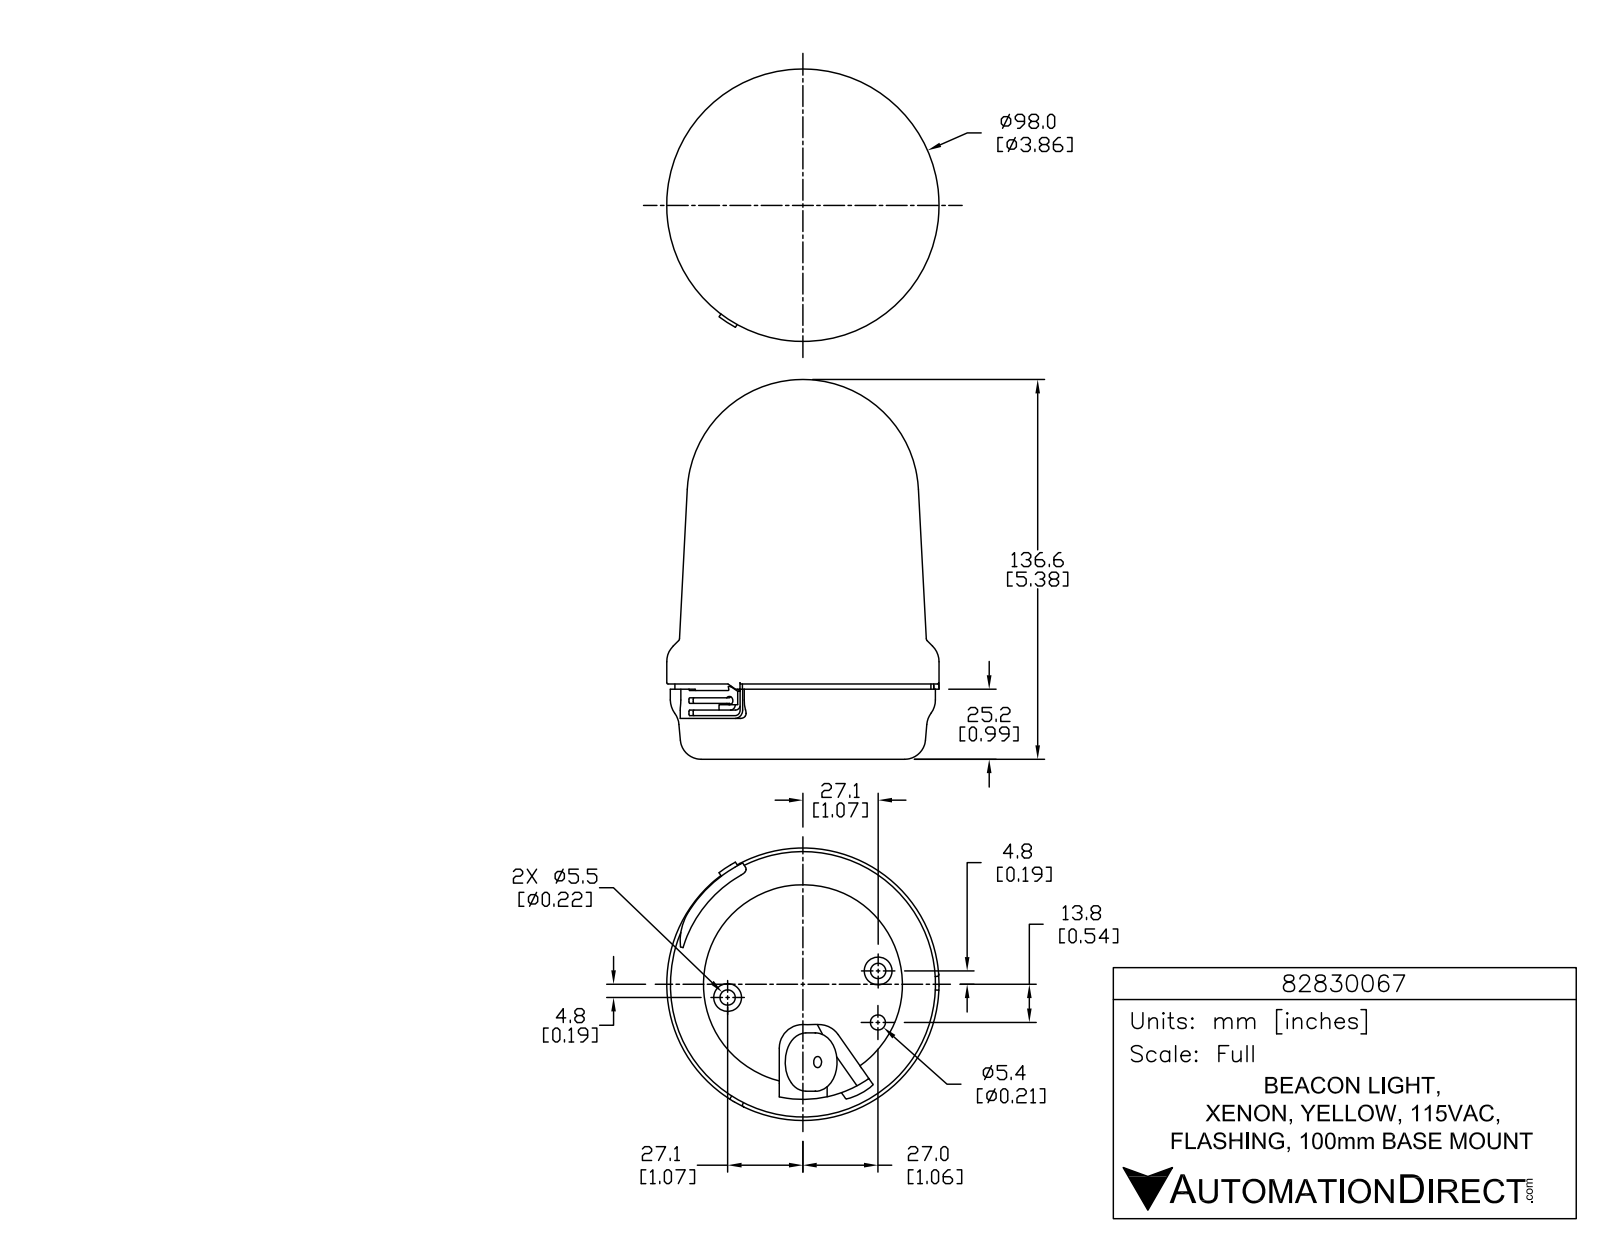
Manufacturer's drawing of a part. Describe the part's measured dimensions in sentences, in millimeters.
The part is named "82830067". Its 3-D file was written by "SolidWorks 2015 (AUTOMOTIVE_DESIGN)". It is 1 solid with 872 faces: 566 planar, 204 cylindrical and 102 other. Overall it measures 136.6 by 98 by 98 millimeters. Its volume is 732 300 cubic millimeters and its surface area 47 520 square millimeters. Round holes: 3 of diameter 1.5, 2 of diameter 5.5, 1 of diameter 4, 1 of diameter 5.4, 1 of diameter 71.6. Round bosses or shafts: 3 of diameter 8.6, 3 of diameter 2.1, 2 of diameter 10, 1 of diameter 98, 1 of diameter 95.4, 1 of diameter 92.1, 1 of diameter 21. Partial cylindrical surfaces (rounded edges, fillets, slot ends): 9 of radius 0.1, 6 of radius 0.1, 6 of radius 0.3, 6 of radius 0.3, 6 of radius 0.3, 6 of radius 5, 5 of radius 0.5, 4 of radius 1. The main face-to-face distances are 26.5, 24.7, 1.9, 0.5, 25.2, 27.1, 6, 14.7, 14.2, 10.5. The hole center spacings are 27.5, 18.5, 30.3, 54.8, 55.
